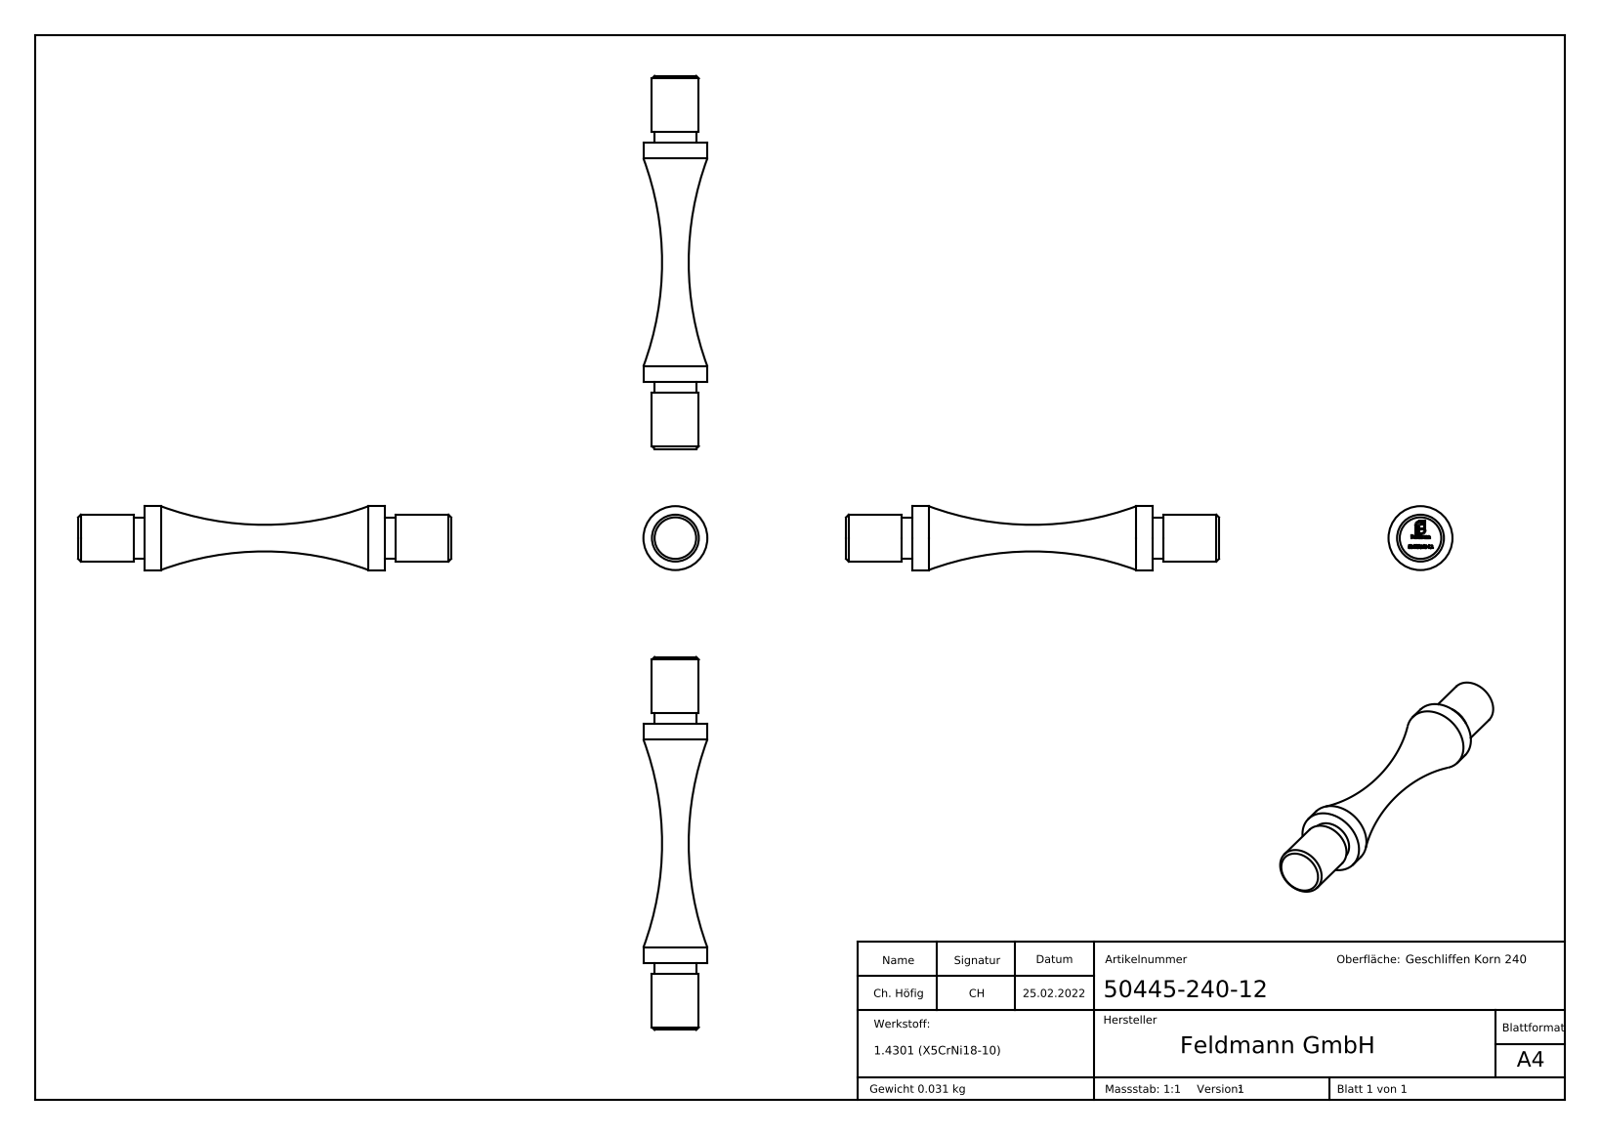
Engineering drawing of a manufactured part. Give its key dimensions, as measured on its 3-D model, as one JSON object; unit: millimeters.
{"part_name": "50445-240-12", "step_written_by": "SolidWorks 2018 (CONFIG_CONTROL_DESIGN)", "units": "millimeters", "bodies": {"solids": 1, "faces": 322, "planar": 188, "cylindrical": 12, "other": 122}, "overall_size": [70, 12, 12], "volume_mm3": 3905, "surface_area_mm2": 2091, "round_bosses_or_shafts": [[12, 1], [8.8, 1], [7.8, 1]], "face_to_face_distances": [12.5, 57.5, 45, 70, 2, 10.5, 59.5, 47, 49, 10.4]}
